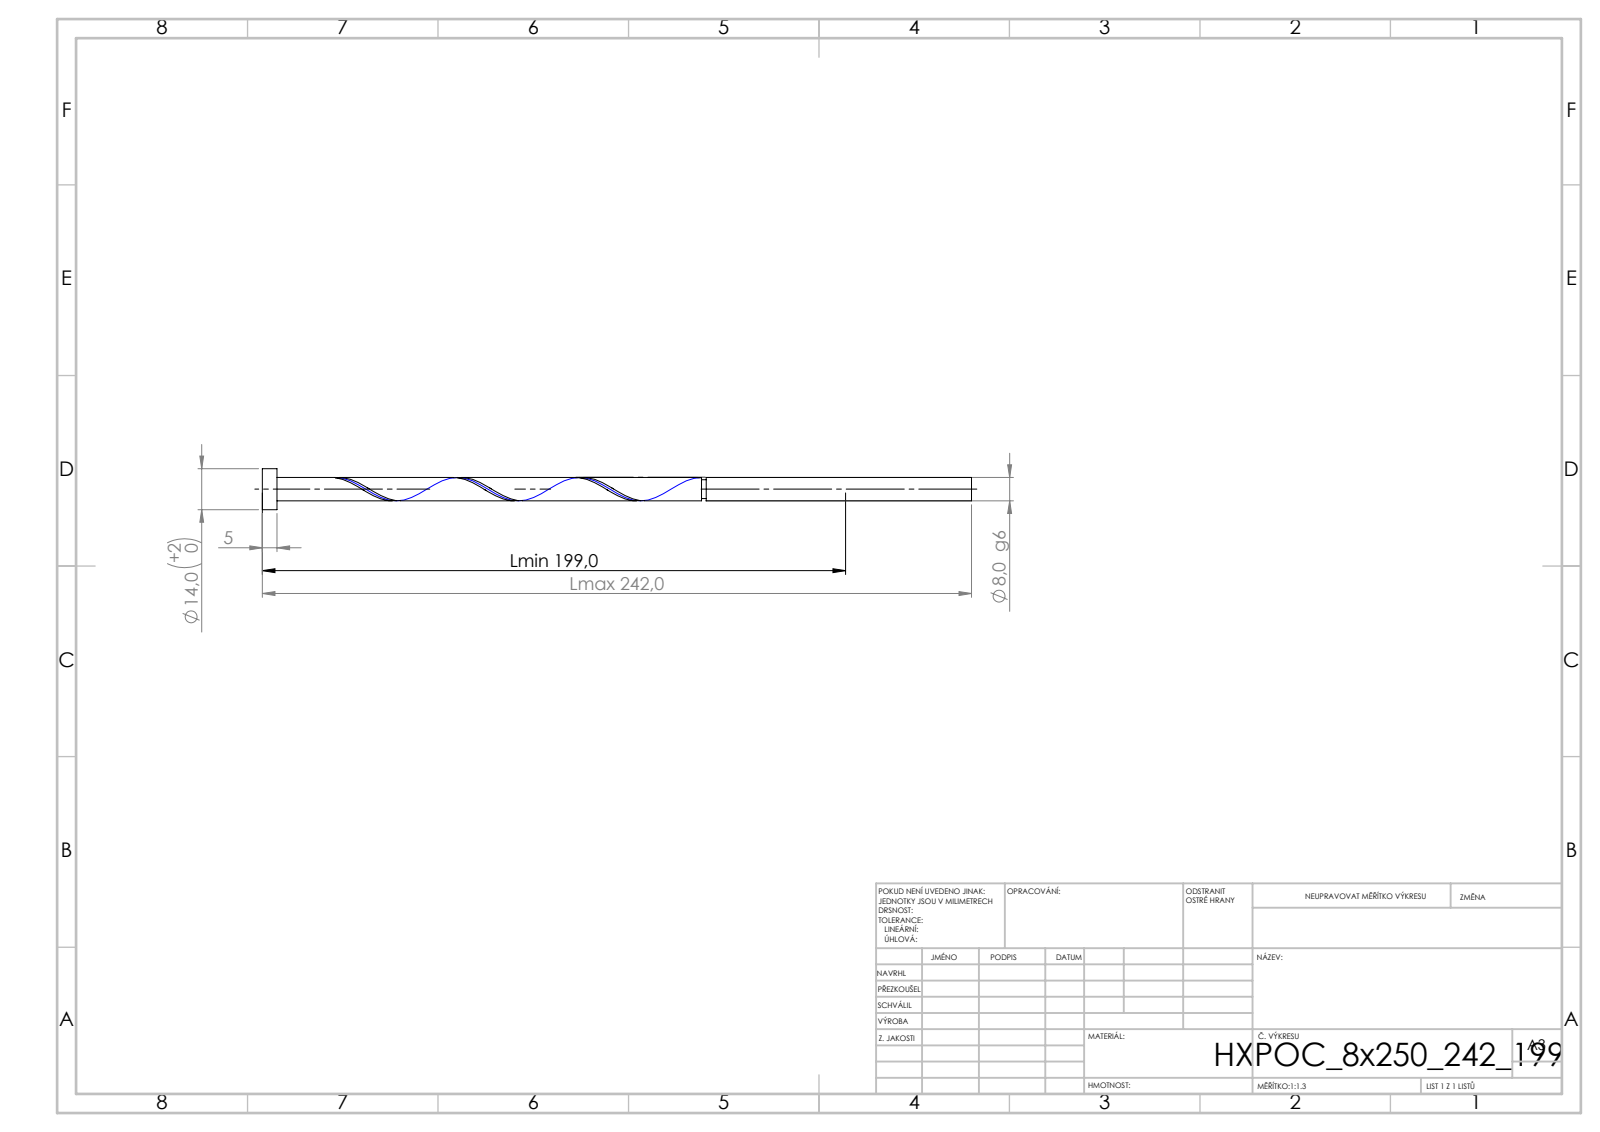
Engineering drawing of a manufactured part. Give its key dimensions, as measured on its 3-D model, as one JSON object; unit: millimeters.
{"step_written_by": "SolidWorks 2019 (CONFIG_CONTROL_DESIGN)", "units": "millimeters", "bodies": {"solids": 1, "faces": 21, "planar": 6, "cylindrical": 14, "other": 1}, "overall_size": [242, 14, 14], "volume_mm3": 12533, "surface_area_mm2": 6630, "round_bosses_or_shafts": [[14, 1], [8, 1], [6.4, 1]], "face_to_face_distances": [5, 242, 237, 151.46, 146.46, 90.54, 149.86, 144.86, 1.6, 92.14]}
